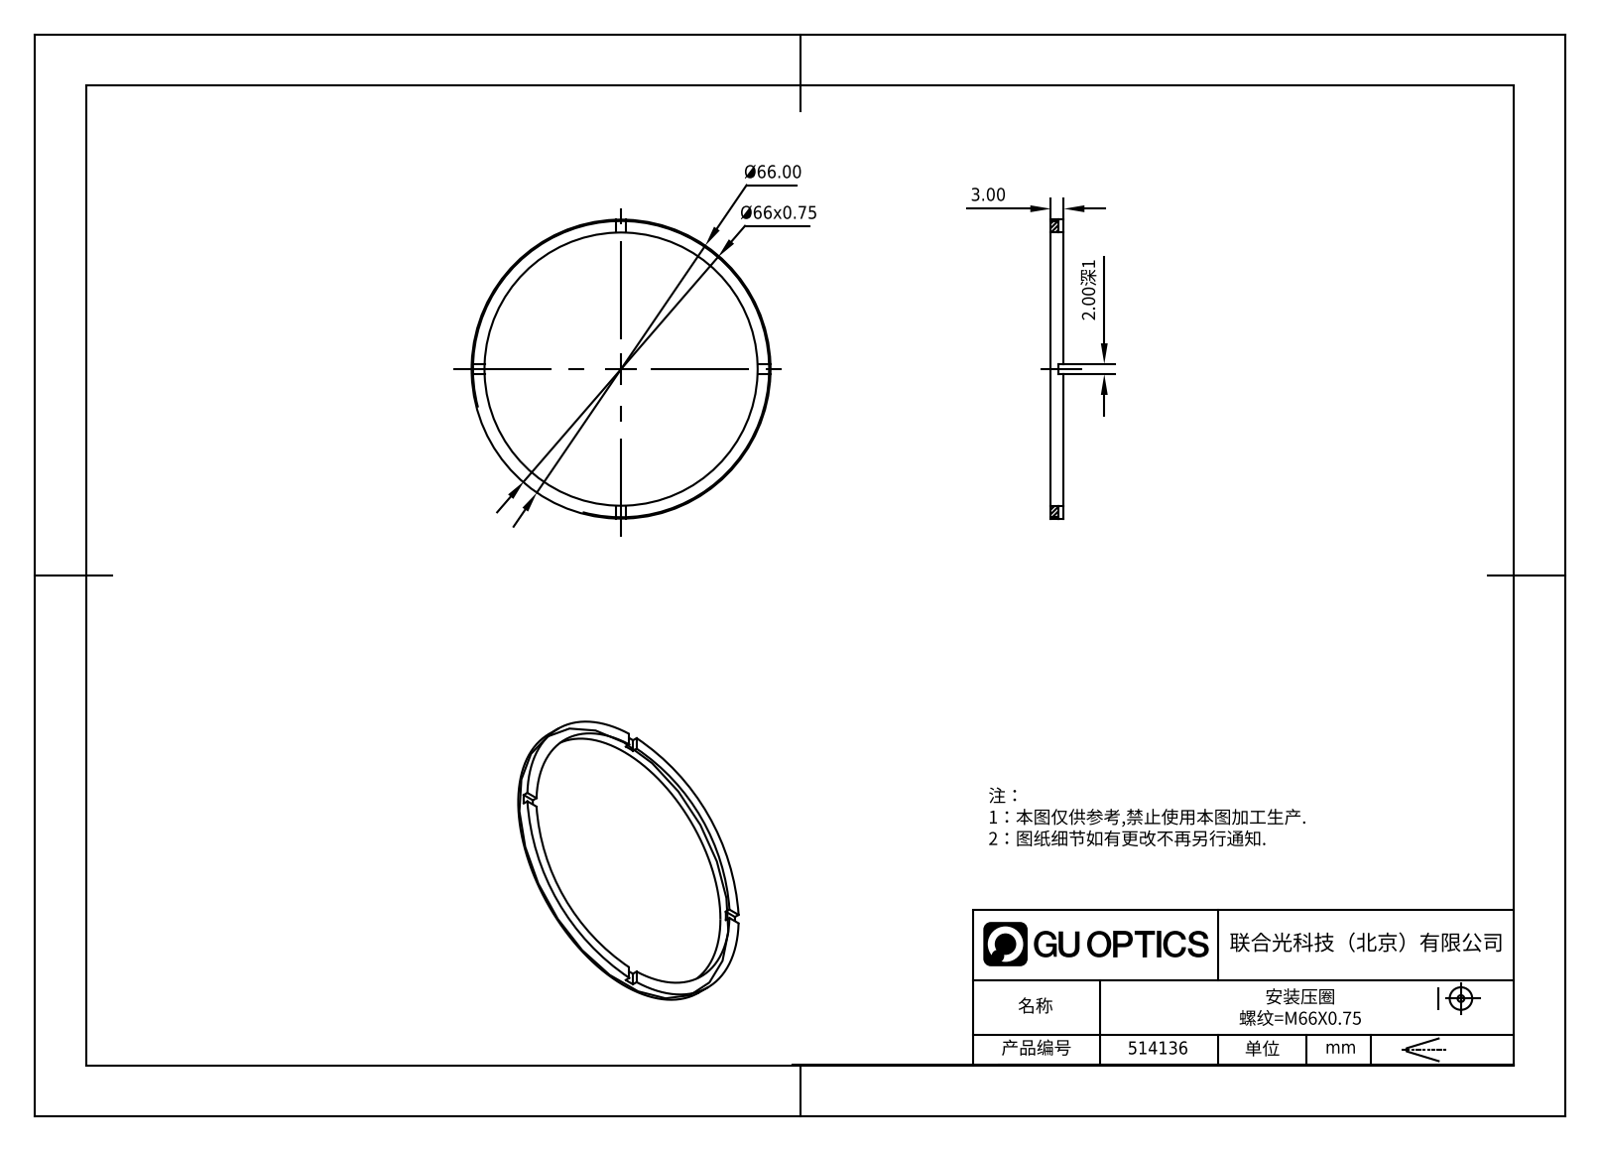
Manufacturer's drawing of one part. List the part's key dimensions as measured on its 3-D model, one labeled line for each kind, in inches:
Part name (STEP PRODUCT): 514136
STEP written by: SolidWorks 2020 (CONFIG_CONTROL_DESIGN)
Units: inches
Bodies: 1 solid, 21 faces (17 planar, 4 cylindrical, 0 other)
Overall size (bounding box): 2.598 × 2.598 × 0.118
Volume: 0.09 in³ · Surface area: 3.407 in²
Round holes (diameter × count): ⌀2.402 ×1
Round bosses / shafts (diameter × count): ⌀2.598 ×1
Main face-to-face distances: 0.118, 0.079, 0.039
